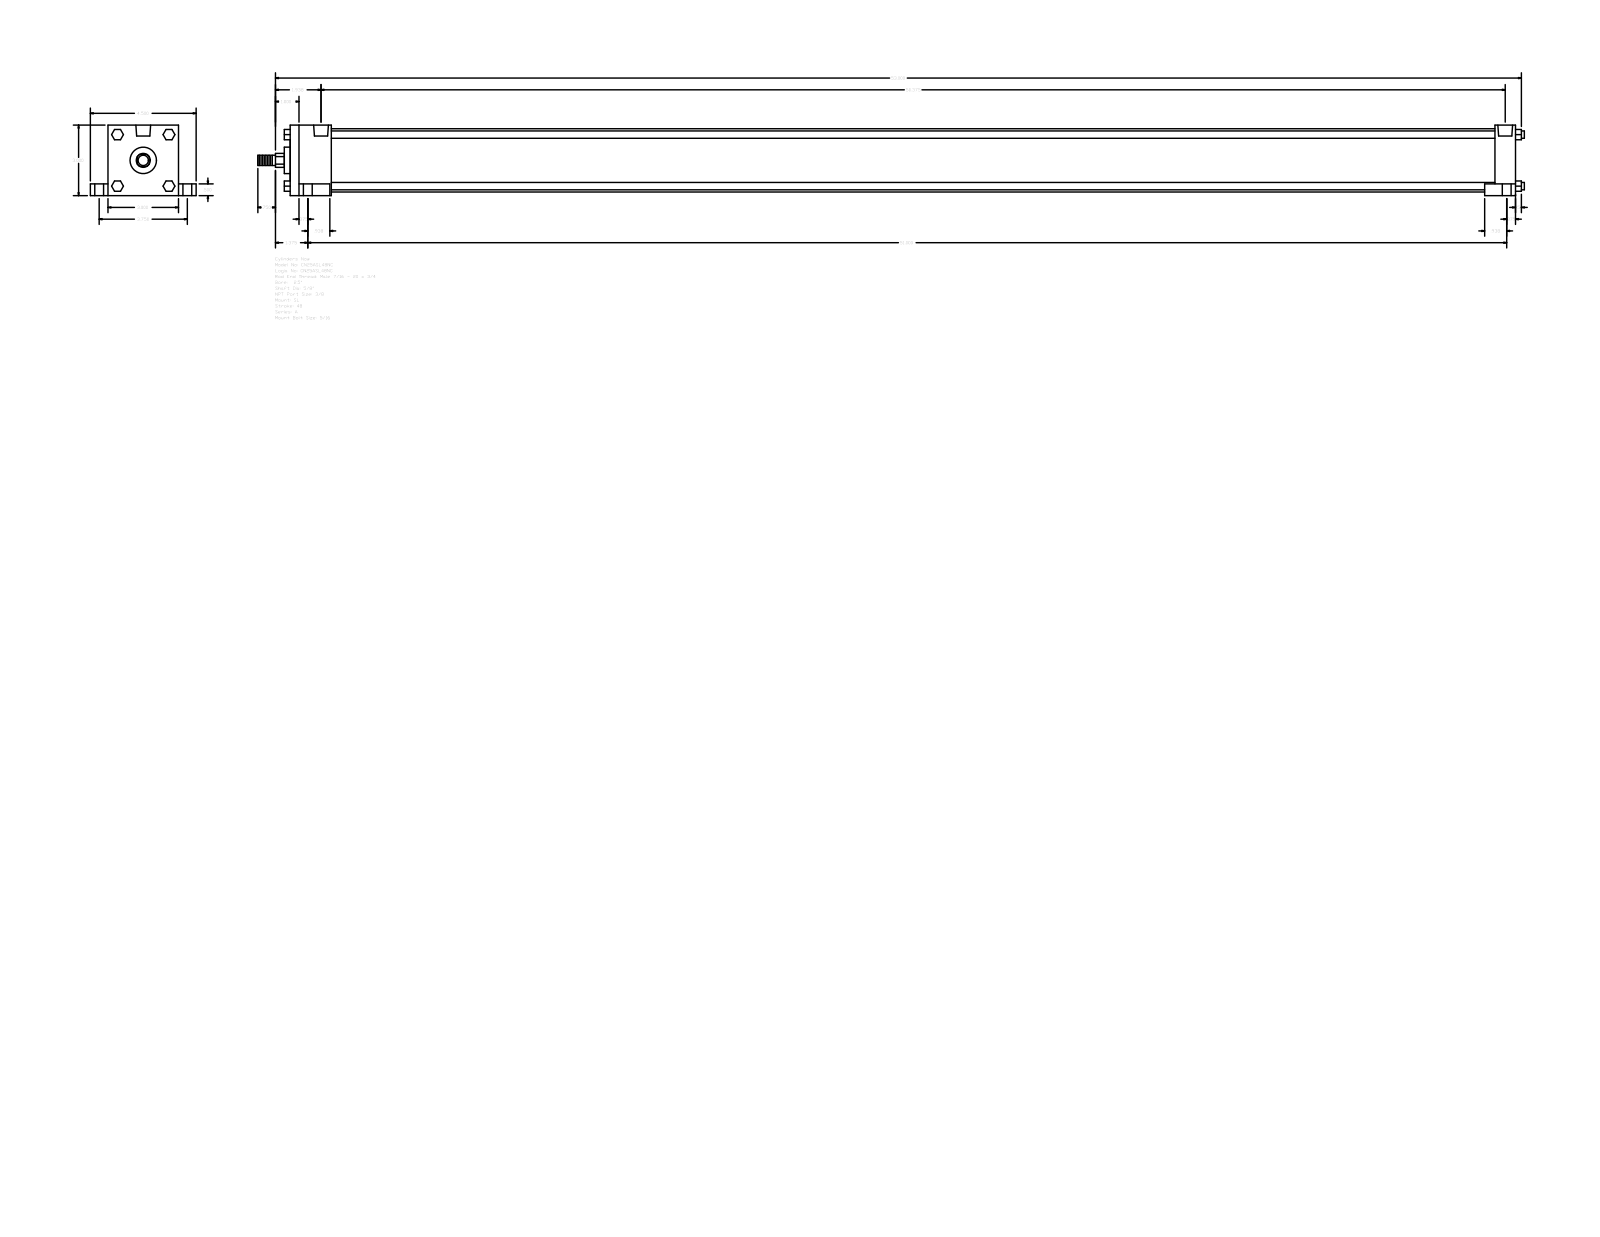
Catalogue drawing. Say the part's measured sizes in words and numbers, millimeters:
The part is named "A_SL__0250_0.625". Its 3-D file was written by "GSSL Pune (CONFIG_CONTROL_DESIGN)". It is 0 solids with 148 faces: 112 planar, 36 cylindrical and 0 other. Overall it measures 1368.42 by 114.3 by 76.2 millimeters. Round holes: 4 of diameter 5.56, 4 of diameter 9.53, 4 of diameter 15.88, 2 of diameter 15.93. Round bosses or shafts: 4 of diameter 7.94, 1 of diameter 68.33, 1 of diameter 28.57, 1 of diameter 15.88, 1 of diameter 11.11. Partial cylindrical surfaces (rounded edges, fillets, slot ends): 1 of radius 7.54. The main face-to-face distances are 76.2, 1323.97, 44.45, 1279.52, 1301.74, 1257.29, 22.23, 63.5, 12.7, 19.05. The hole center spacings are 2.38, 47.63, 47.65, 49.09, 49.72, 95.24, 1281.91, 1282.
